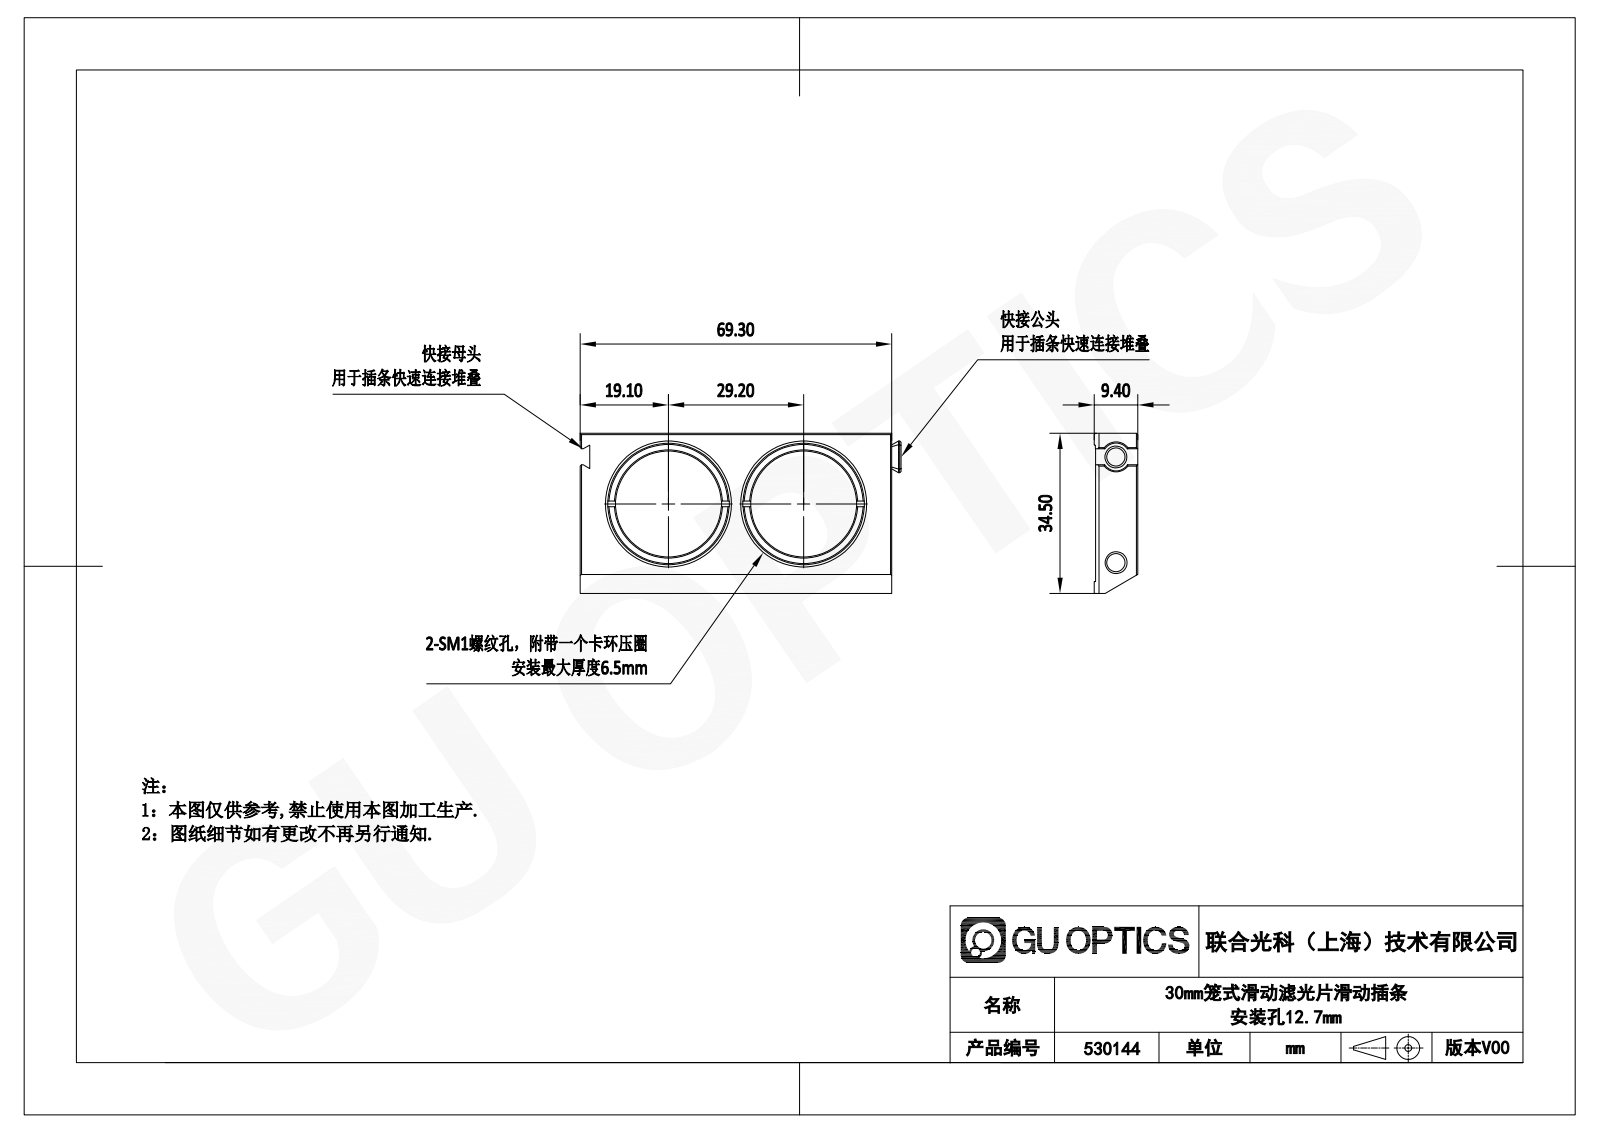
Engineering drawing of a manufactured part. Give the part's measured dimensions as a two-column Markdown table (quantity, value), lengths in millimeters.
| quantity | value |
| --- | --- |
| part name | 530144 |
| STEP written by | SolidWorks 2020 (CONFIG_CONTROL_DESIGN) |
| units | millimeters |
| bodies | 3 solids, 130 faces (83 planar, 18 cylindrical, 29 other) |
| overall size | 69.29 × 34.54 × 9.4 |
| volume | 10 726 mm³ |
| surface area | 7 398 mm² |
| round holes (diameter × count) | 4 × 2, 4.8 × 2, 22.9 × 2, 24 × 2, 26.29 × 1, 26.29 × 1, 27.29 × 1, 27.29 × 1 |
| round bosses / shafts (diameter × count) | 26.29 × 1 |
| partial cylindrical surfaces (radius × count) | 3 × 1, 3.43 × 1 |
| main face-to-face distances | 9.09, 9.39, 0.9, 8.49, 0.6, 67.31, 7.09, 7.39, 6.49, 2 |
| hole center spacings | 22.86, 29.21 |
